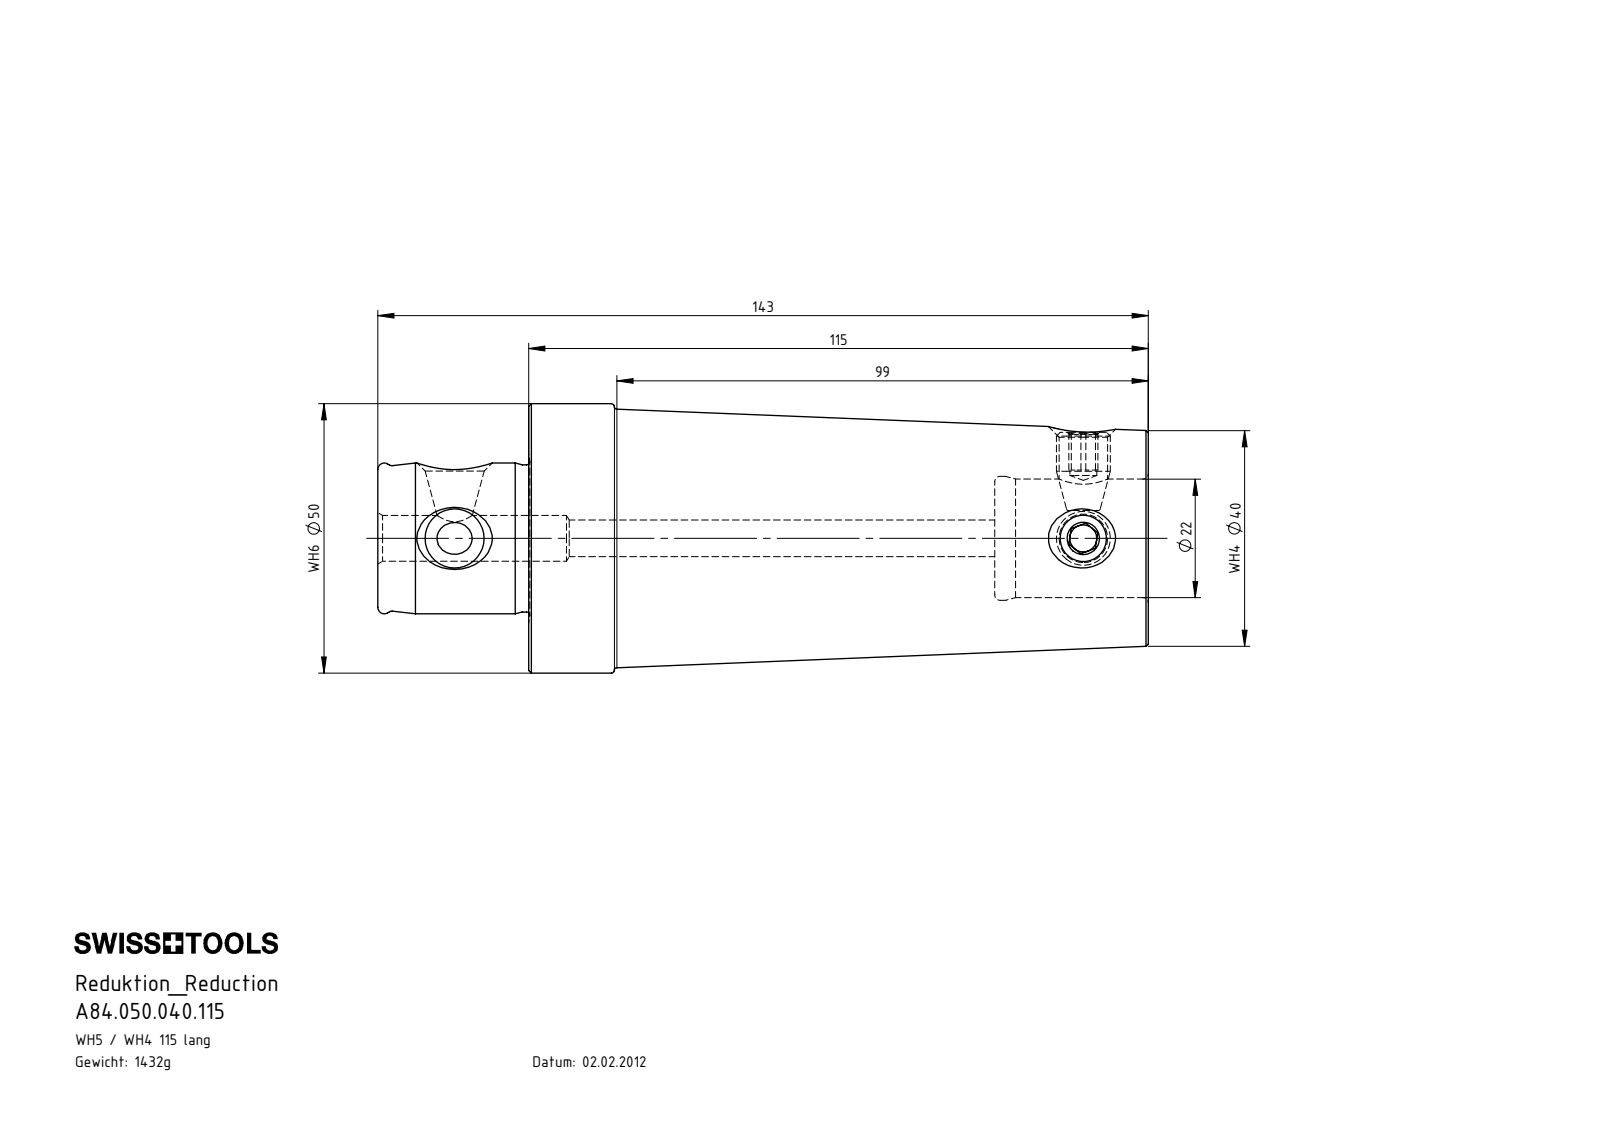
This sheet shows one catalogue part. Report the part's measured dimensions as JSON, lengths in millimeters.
{"part_name": "WH4-ER1.001.015; A84.050.040.115; WH5-WH4.K01.115_B", "step_written_by": "SolidWorks 2017 (CONFIG_CONTROL_DESIGN)", "units": "millimeters", "bodies": {"solids": 3, "faces": 132, "planar": 32, "cylindrical": 26, "other": 74}, "overall_size": [143, 50, 50], "volume_mm3": 182434, "surface_area_mm2": 28179, "round_holes": [[5, 2], [9, 2], [6.8, 1], [8.5, 1], [22, 1], [23, 1]], "round_bosses_or_shafts": [[10, 2], [50, 1], [28, 1], [27.3, 1]], "face_to_face_distances": [115, 28, 143, 114.5, 86.5, 28.5, 5, 14.5, 7.5, 7]}
